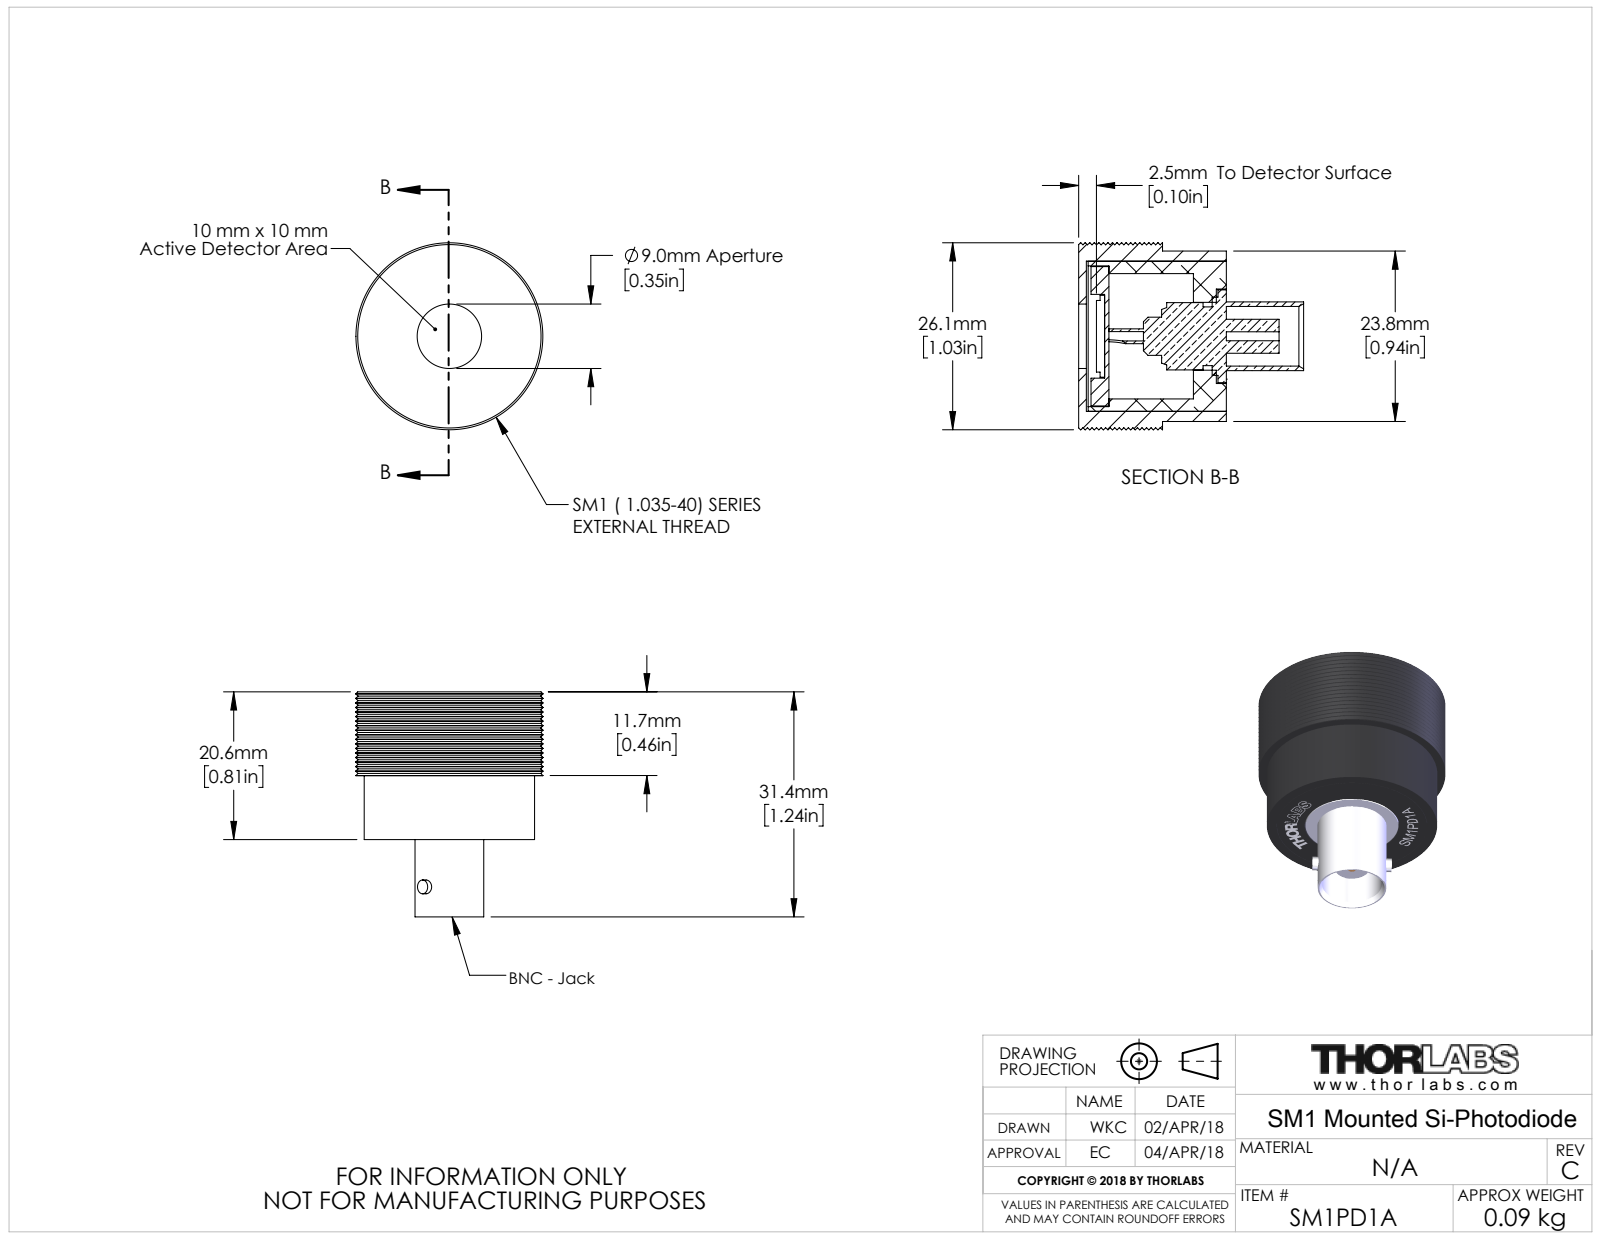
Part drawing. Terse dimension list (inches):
name: TTN008836-E0W
written by: SolidWorks 2016 (AUTOMOTIVE_DESIGN)
unit: in
bodies: 5 solids, 406 faces (218 planar, 43 cylindrical, 145 other)
size: 1.237 × 1.028 × 1.028
volume: 0.45 in³; area: 14.78 in²
holes: 1× ⌀0.05, 1× ⌀0.052, 1× ⌀0.328, 1× ⌀0.354, 1× ⌀0.373, 1× ⌀0.52, 1× ⌀0.689, 1× ⌀0.774, 1× ⌀0.827
bosses: 1× ⌀1.028, 1× ⌀0.937, 1× ⌀0.824, 1× ⌀0.766, 1× ⌀0.51, 1× ⌀0.43, 1× ⌀0.378, 1× ⌀0.37
rounds: 2× R0.039
face distances: 0.812, 0.646, 0.167, 0.669, 0.024, 0.143, 0.77, 0.124, 0.101, 0.042
